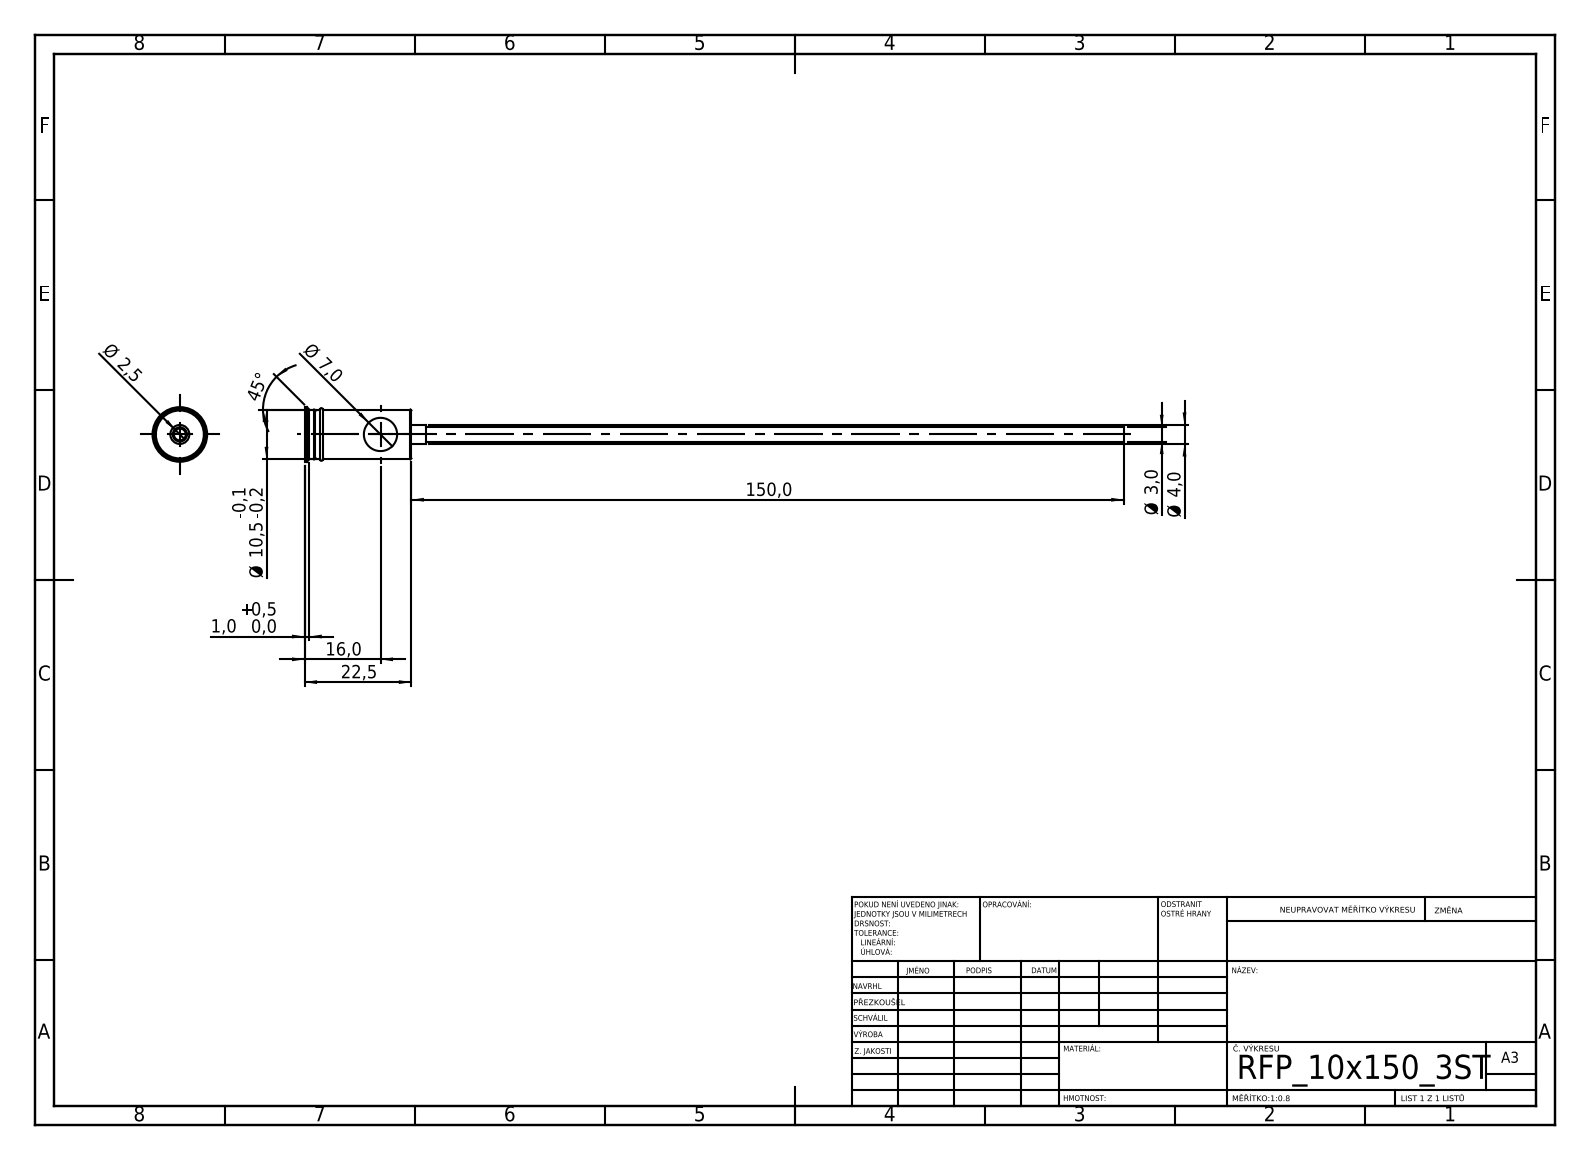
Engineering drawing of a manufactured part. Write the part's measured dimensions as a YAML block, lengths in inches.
step_written_by: "SolidWorks 2019 (CONFIG_CONTROL_DESIGN)"
units: inches
bodies: {solids: 1, faces: 44, planar: 20, cylindrical: 16, other: 8}
overall_size: [6.791, 0.453, 0.453]
volume: 0.113
surface_area: 5.797
round_holes:
  - {diameter: 0.098, count: 1}
  - {diameter: 0.276, count: 1}
round_bosses_or_shafts:
  - {diameter: 0.453, count: 1}
  - {diameter: 0.413, count: 1}
  - {diameter: 0.157, count: 1}
  - {diameter: 0.118, count: 1}
face_to_face_distances: [0.886, 0.807, 0.079, 0.232, 0.795, 0.091, 0.118, 0.913, 0.925, 1.004]
